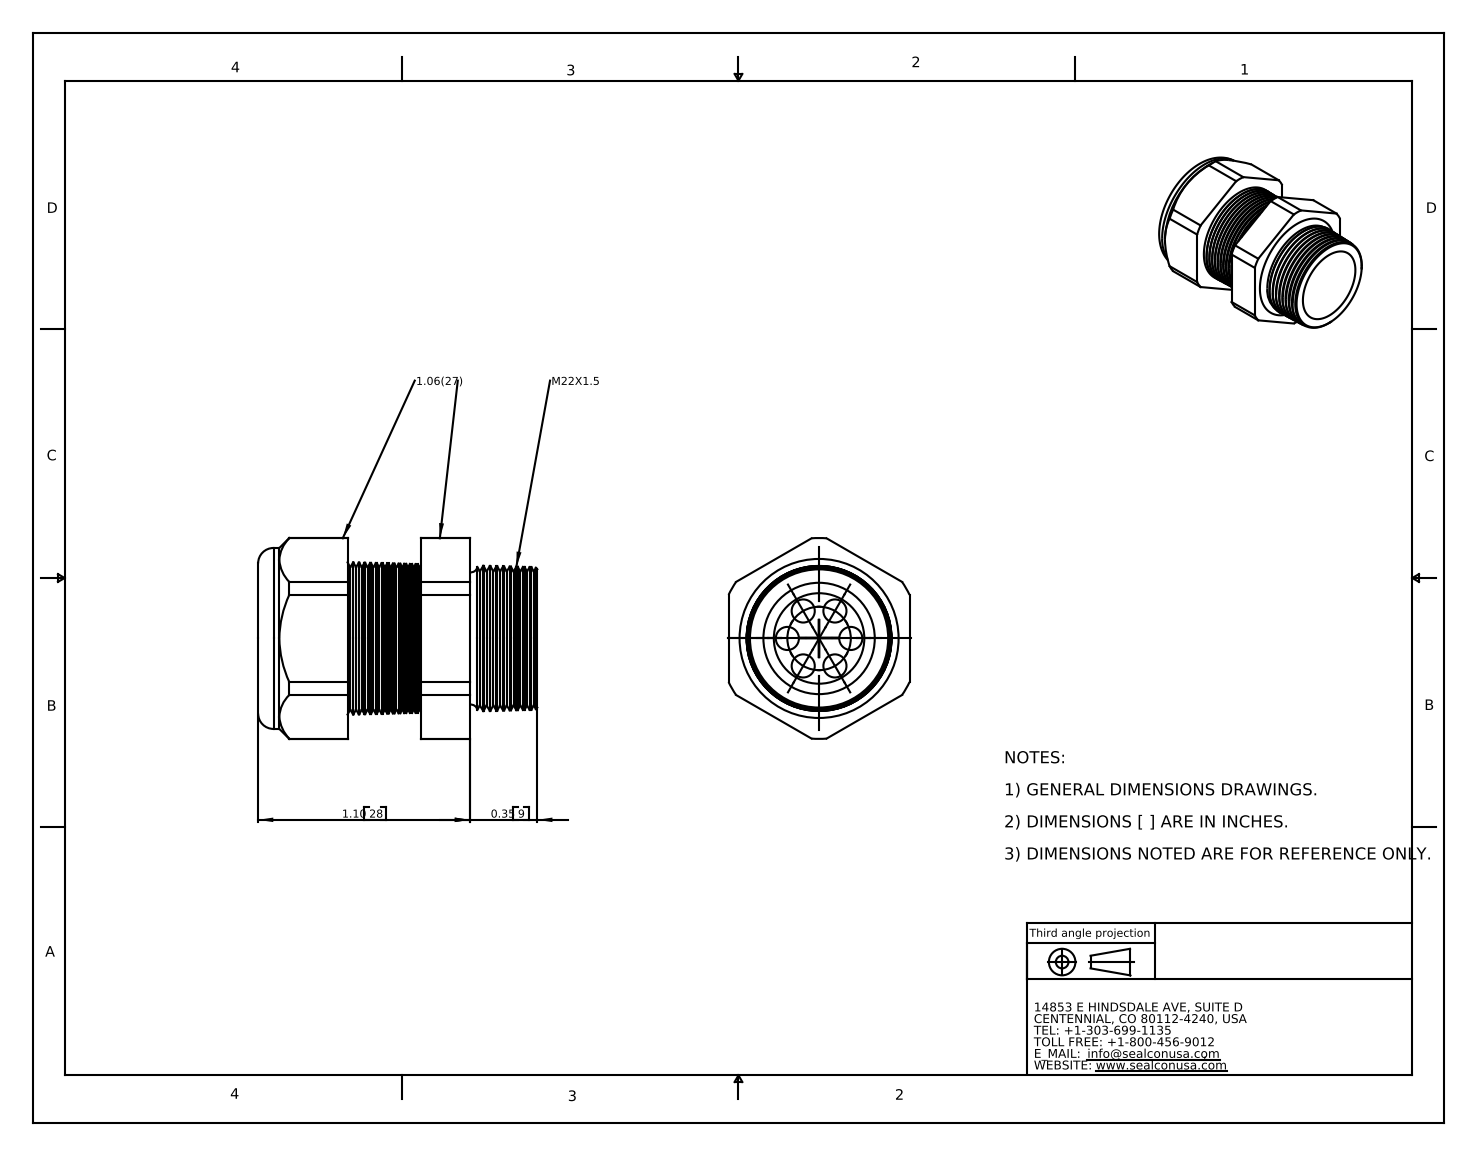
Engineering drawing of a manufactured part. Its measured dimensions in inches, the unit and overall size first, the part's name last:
Units: inches
Overall size (bounding box): 1.45 × 1.043 × 0.94
Round holes (diameter × count): ⌀0.12 ×6, ⌀0.45 ×1, ⌀0.47 ×1
Round bosses / shafts (diameter × count): ⌀0.94 ×1
Partial cylindrical surfaces — rounded edges, fillets, slot ends (radius × count): R0.522 ×1
Main face-to-face distances: 0.94, 0.844, 0.465, 0.38, 1.1, 0.635, 0.256, 1.45, 0.985, 0.606
Hole centre spacings: 0.165, 0.285, 0.329
Volume: 0.579 in³ · Surface area: 10.41 in²
Bodies: 2 solids, 198 faces (20 planar, 32 cylindrical, 146 other)
Part name (STEP PRODUCT): CD22M0-BK
STEP written by: SolidWorks 2007 (CONFIG_CONTROL_DESIGN)
